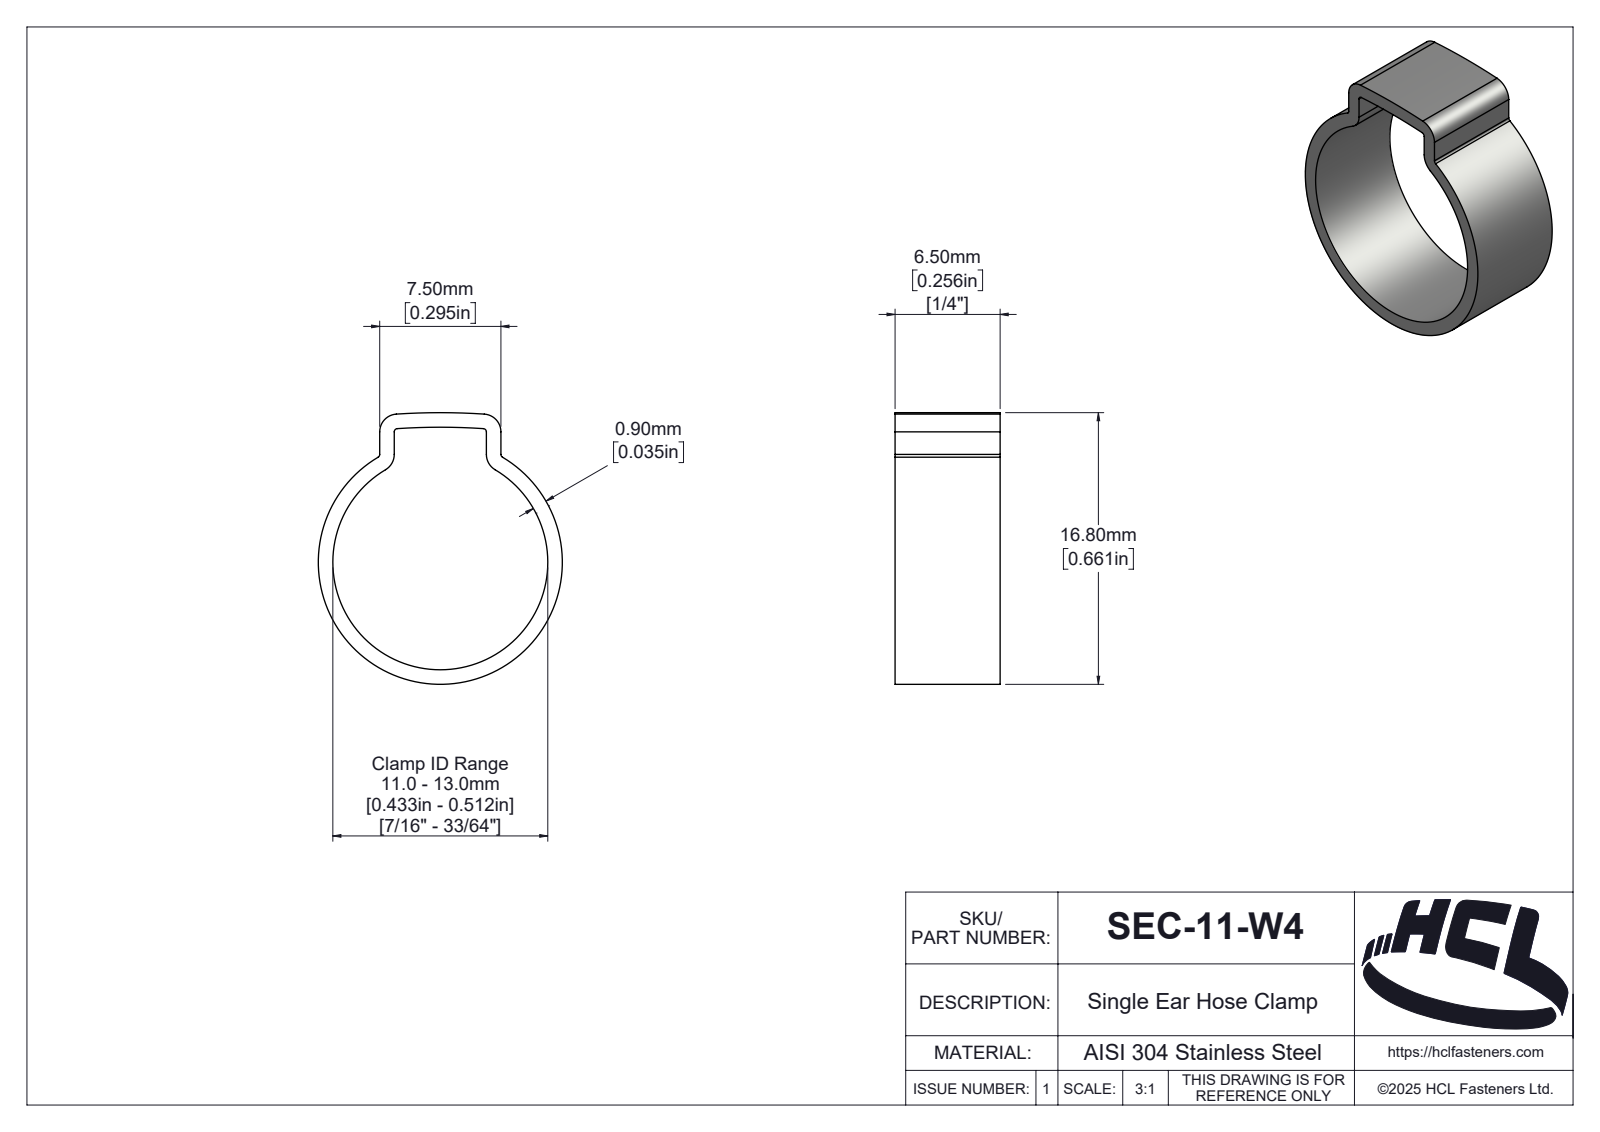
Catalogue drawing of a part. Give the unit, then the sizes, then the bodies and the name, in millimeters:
Units: millimetres
Overall size (bounding box): 16.8 × 15.1 × 6.5
Round holes (diameter × count): ⌀13.3 ×1
Round bosses / shafts (diameter × count): ⌀15.1 ×1
Partial cylindrical surfaces — rounded edges, fillets, slot ends (radius × count): R0.2 ×4, R1.1 ×4, R0.2 ×1, R0.81 ×1, R1.01 ×1, R1.06 ×1, R1.28 ×1, R1.81 ×1
Main face-to-face distances: 6.5, 0.9, 6.6, 7.5, 5.7, 3.48, 2.58, 3.12, 4.02, 3.63
Volume: 283 mm³ · Surface area: 722 mm²
Bodies: 1 solid, 123 faces (8 planar, 66 cylindrical, 49 other)
Part name (STEP PRODUCT): SEC-11-W4
STEP written by: SolidWorks 2025 (AUTOMOTIVE_DESIGN)
